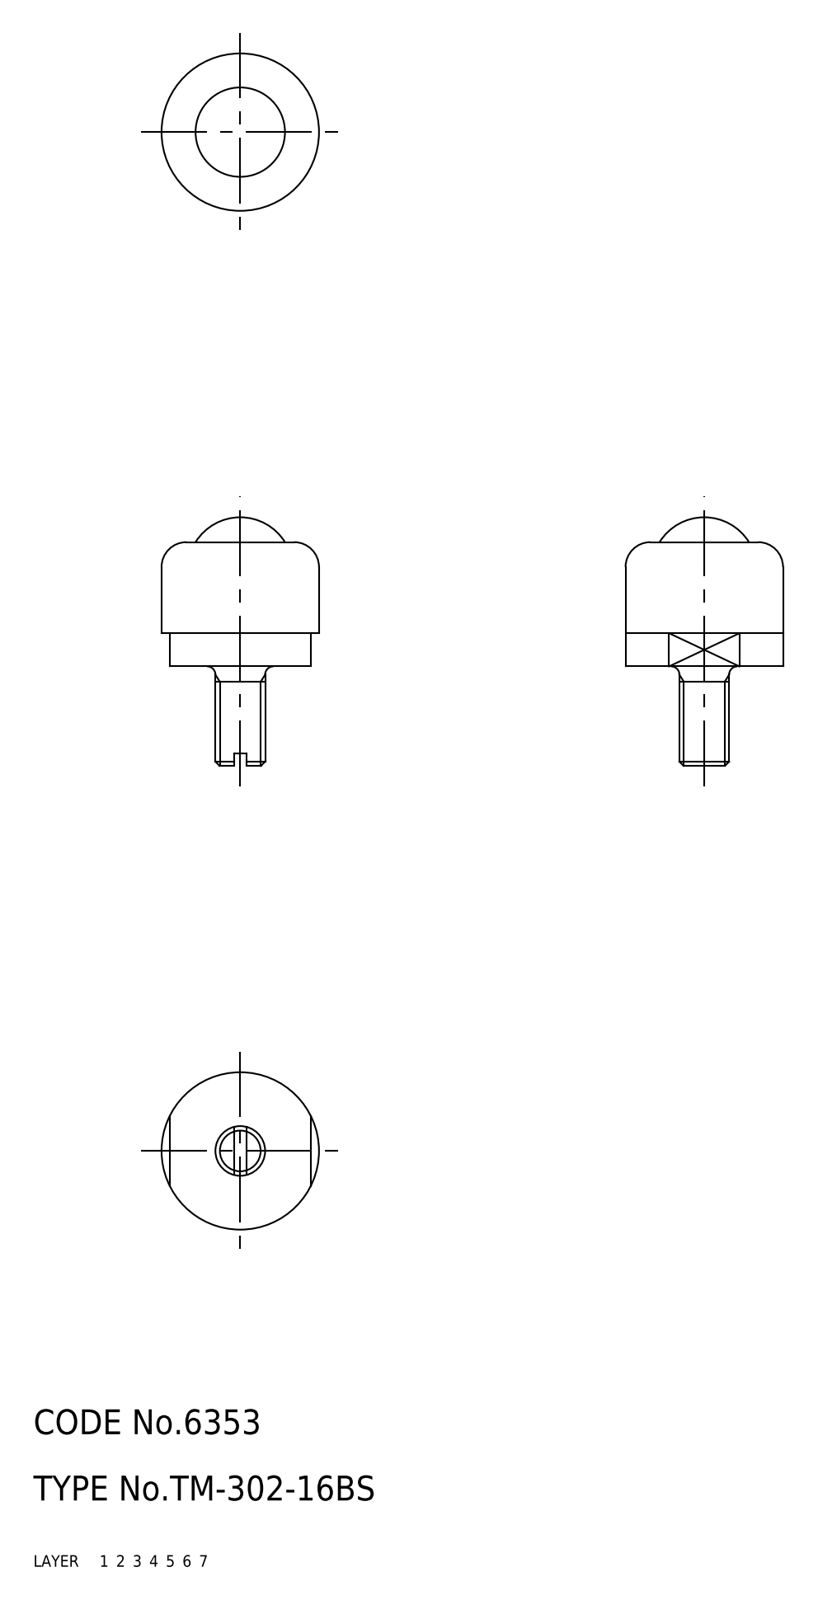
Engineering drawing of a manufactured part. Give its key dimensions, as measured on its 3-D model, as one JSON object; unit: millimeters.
{"part_name": "67111099; 67111112; 67111125", "step_written_by": "CADfix (AUTOMOTIVE_DESIGN)", "units": "millimeters", "bodies": {"solids": 3, "faces": 32, "planar": 0, "cylindrical": 0, "other": 32}, "overall_size": [30, 19, 19], "volume_mm3": 2982, "surface_area_mm2": 2986}
